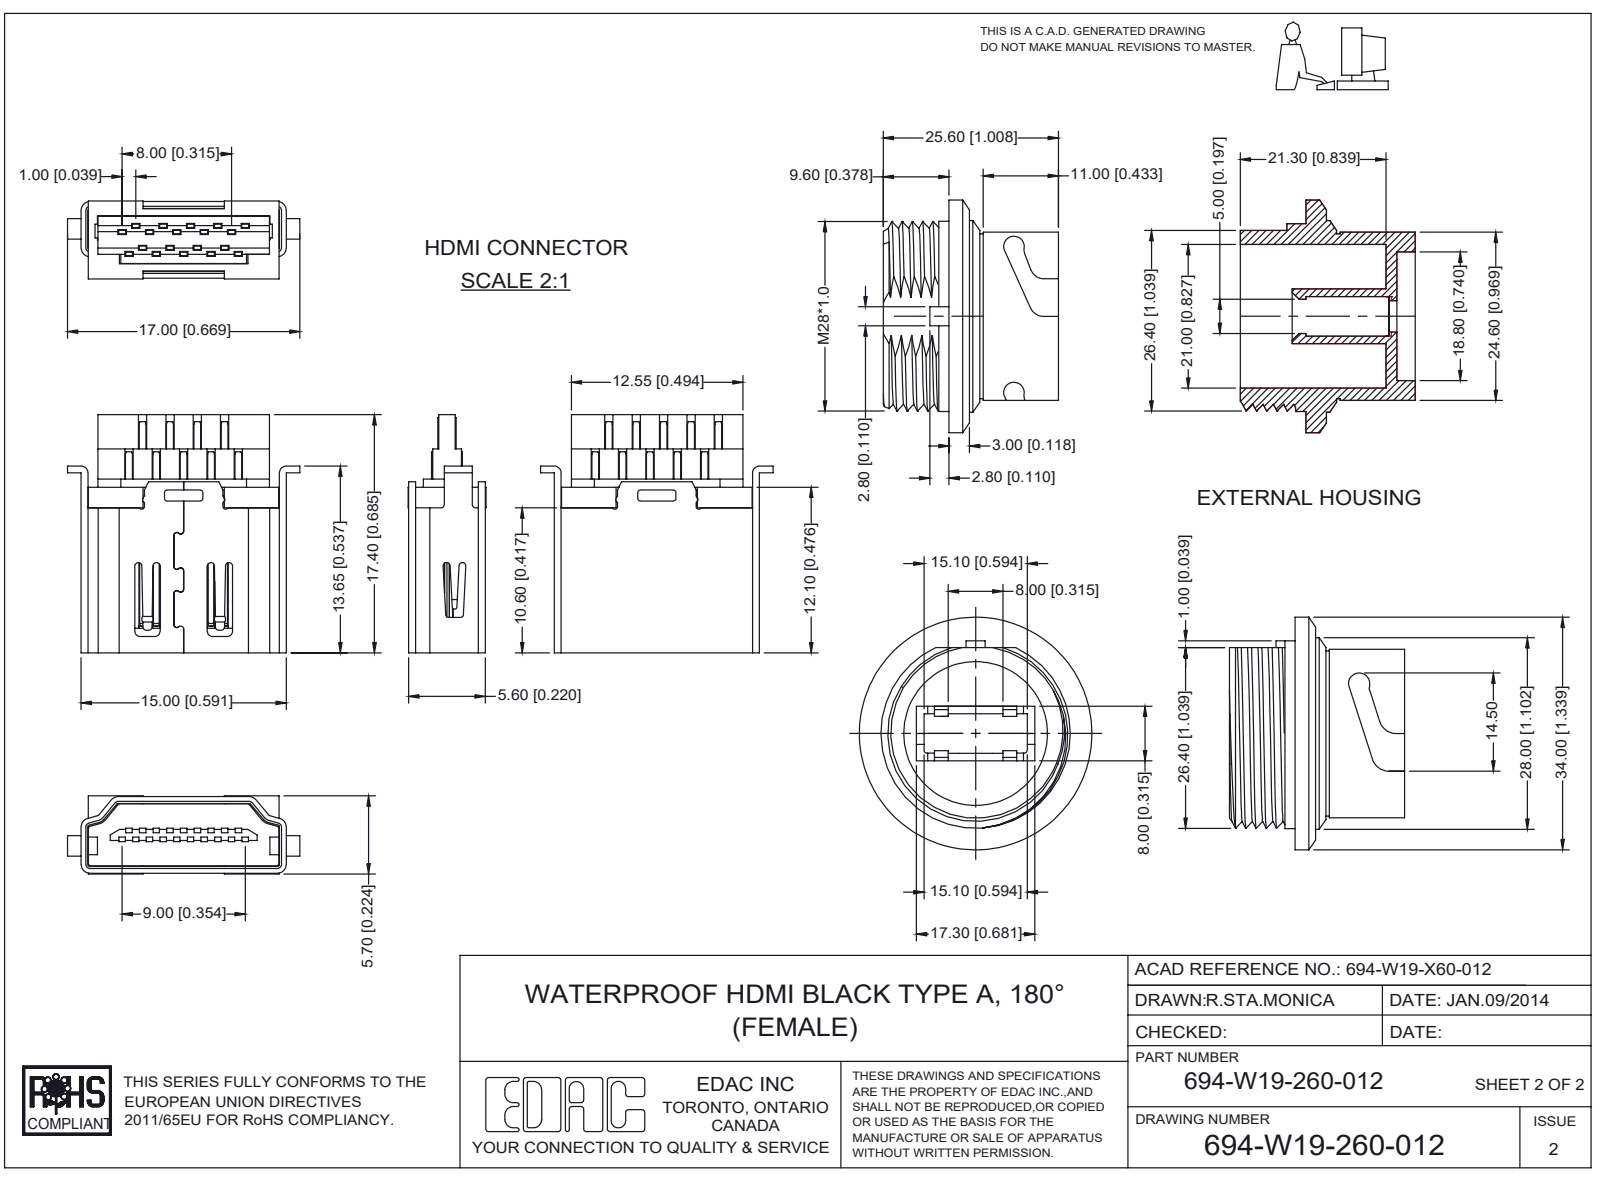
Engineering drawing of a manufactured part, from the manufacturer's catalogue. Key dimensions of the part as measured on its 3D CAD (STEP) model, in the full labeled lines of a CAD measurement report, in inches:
Part name (STEP PRODUCT): HDMI ASSY 694-W19-X60-012; HDMI CONTACT2 694-W19-X60-012; HDMI HOUSING2 694-W19-X60-012; HOUSING 694-W19-X60-012 (+4 more)
STEP written by: SolidWorks 2020 (AUTOMOTIVE_DESIGN)
Units: inches
Bodies: 23 solids, 1962 faces (1365 planar, 542 cylindrical, 55 other)
Overall size (bounding box): 1.339 × 1.339 × 1.008
Volume: 0.45 in³ · Surface area: 15.08 in²
Round holes (diameter × count): ⌀0.74 ×1, ⌀0.827 ×1
Round bosses / shafts (diameter × count): ⌀1.339 ×1, ⌀1.102 ×1, ⌀1.094 ×1, ⌀0.969 ×1, ⌀0.949 ×1
Partial cylindrical surfaces — rounded edges, fillets, slot ends (radius × count): R0.006 ×240, R0.008 ×38, R0.008 ×28, R0.02 ×12, R0.01 ×10, R0.004 ×6, R0.014 ×6, R0.026 ×6
Main face-to-face distances: 0.106, 0.02, 0.043, 0.022, 0.272, 0.378, 0.118, 0.063, 0.075, 0.315
